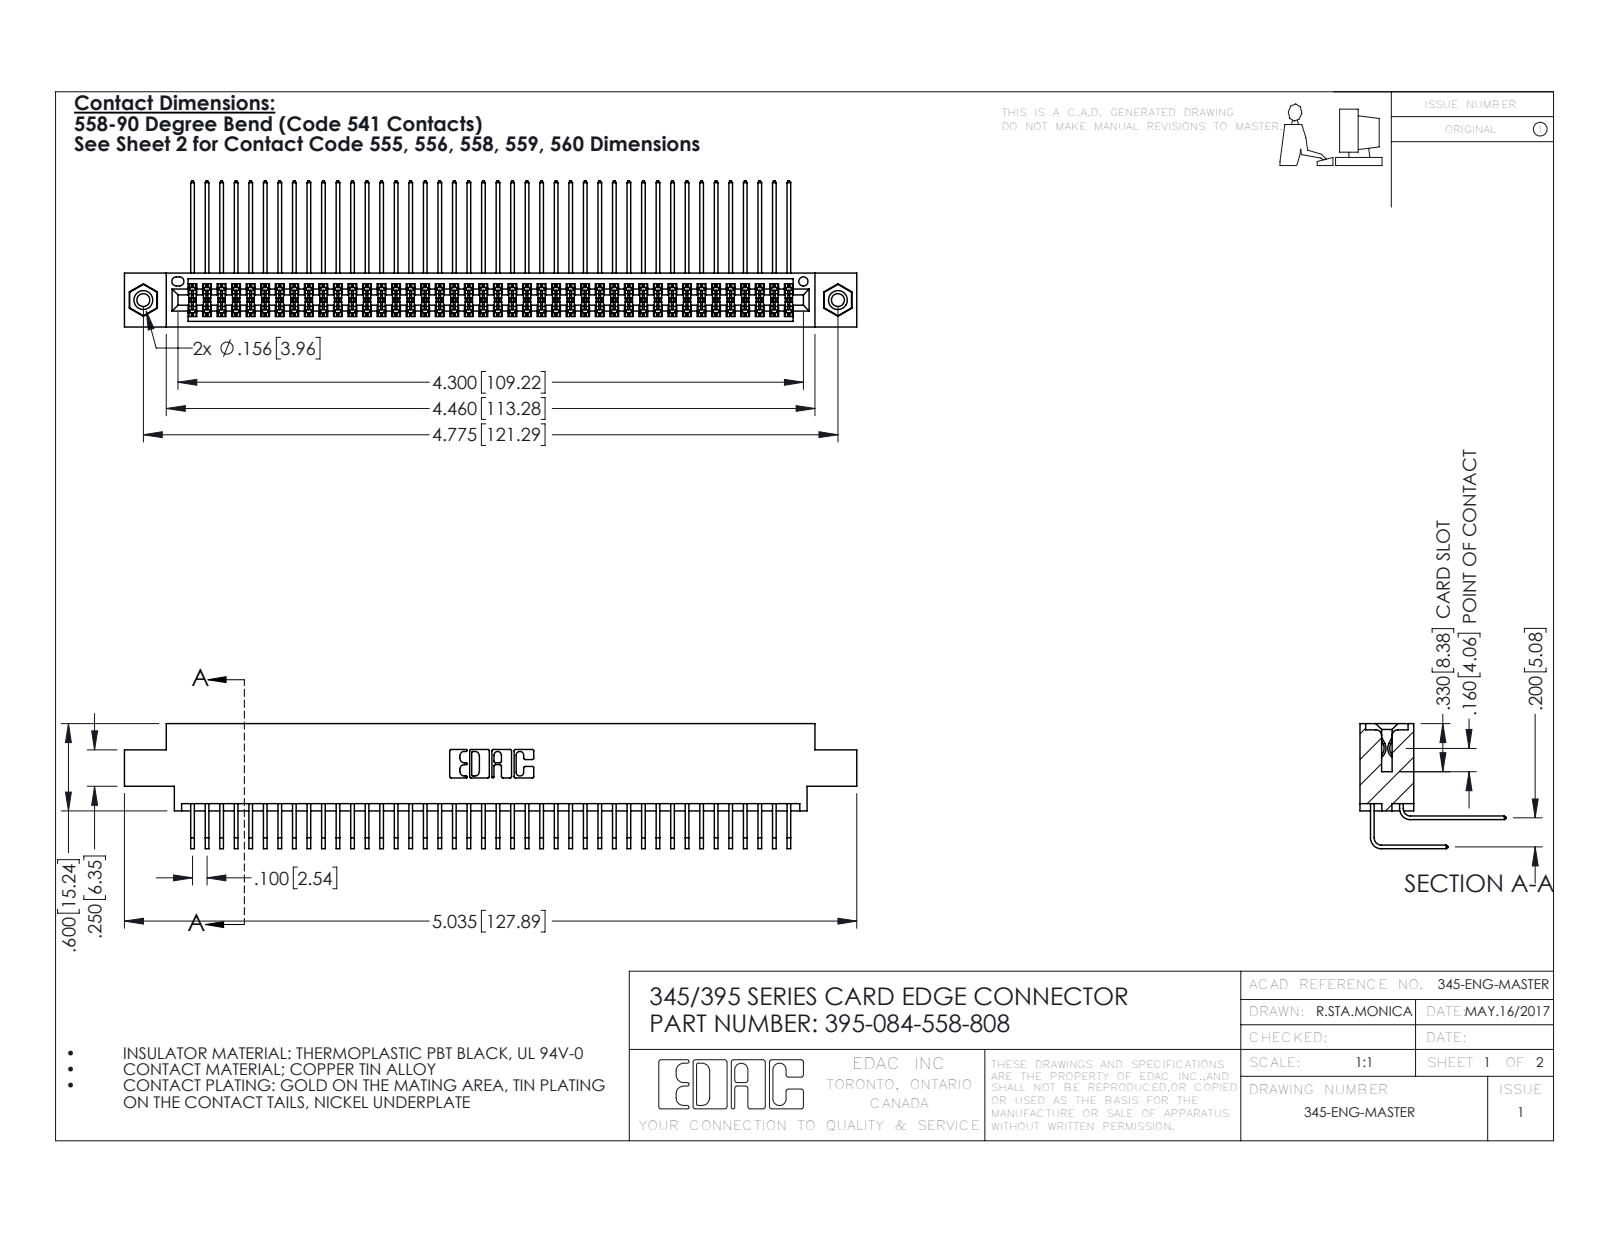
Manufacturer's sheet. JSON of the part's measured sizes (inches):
{"part_name": "345-250-001_345-250-003-102; 345-292-001_558 559 Tail - 1; 395-084-558-808; 345 Part_0.170 Offset - 0.156 Dia-TI (+1 more)", "step_written_by": "SolidWorks 2016 (CONFIG_CONTROL_DESIGN)", "units": "inches", "bodies": {"solids": 87, "faces": 4558, "planar": 3056, "cylindrical": 1486, "other": 16}, "overall_size": [5.035, 1.005, 0.859], "volume_in3": 0.78, "surface_area_in2": 33.07, "round_holes": [[0.089, 2], [0.125, 2], [0.156, 2], [0.064, 1]], "round_bosses_or_shafts": [[0.155, 2]], "partial_cylinders_radius": [[0.006, 127], [0.01, 22], [0.007, 6], [0.031, 6], [0.026, 3], [0.014, 2], [0.019, 2], [0.022, 2]], "face_to_face_distances": [0.072, 0.298, 0.2, 0.37, 0.098, 0.272, 0.025, 0.225, 0.175, 0.025], "hole_center_spacings": [0.27, 4.539, 4.775]}
